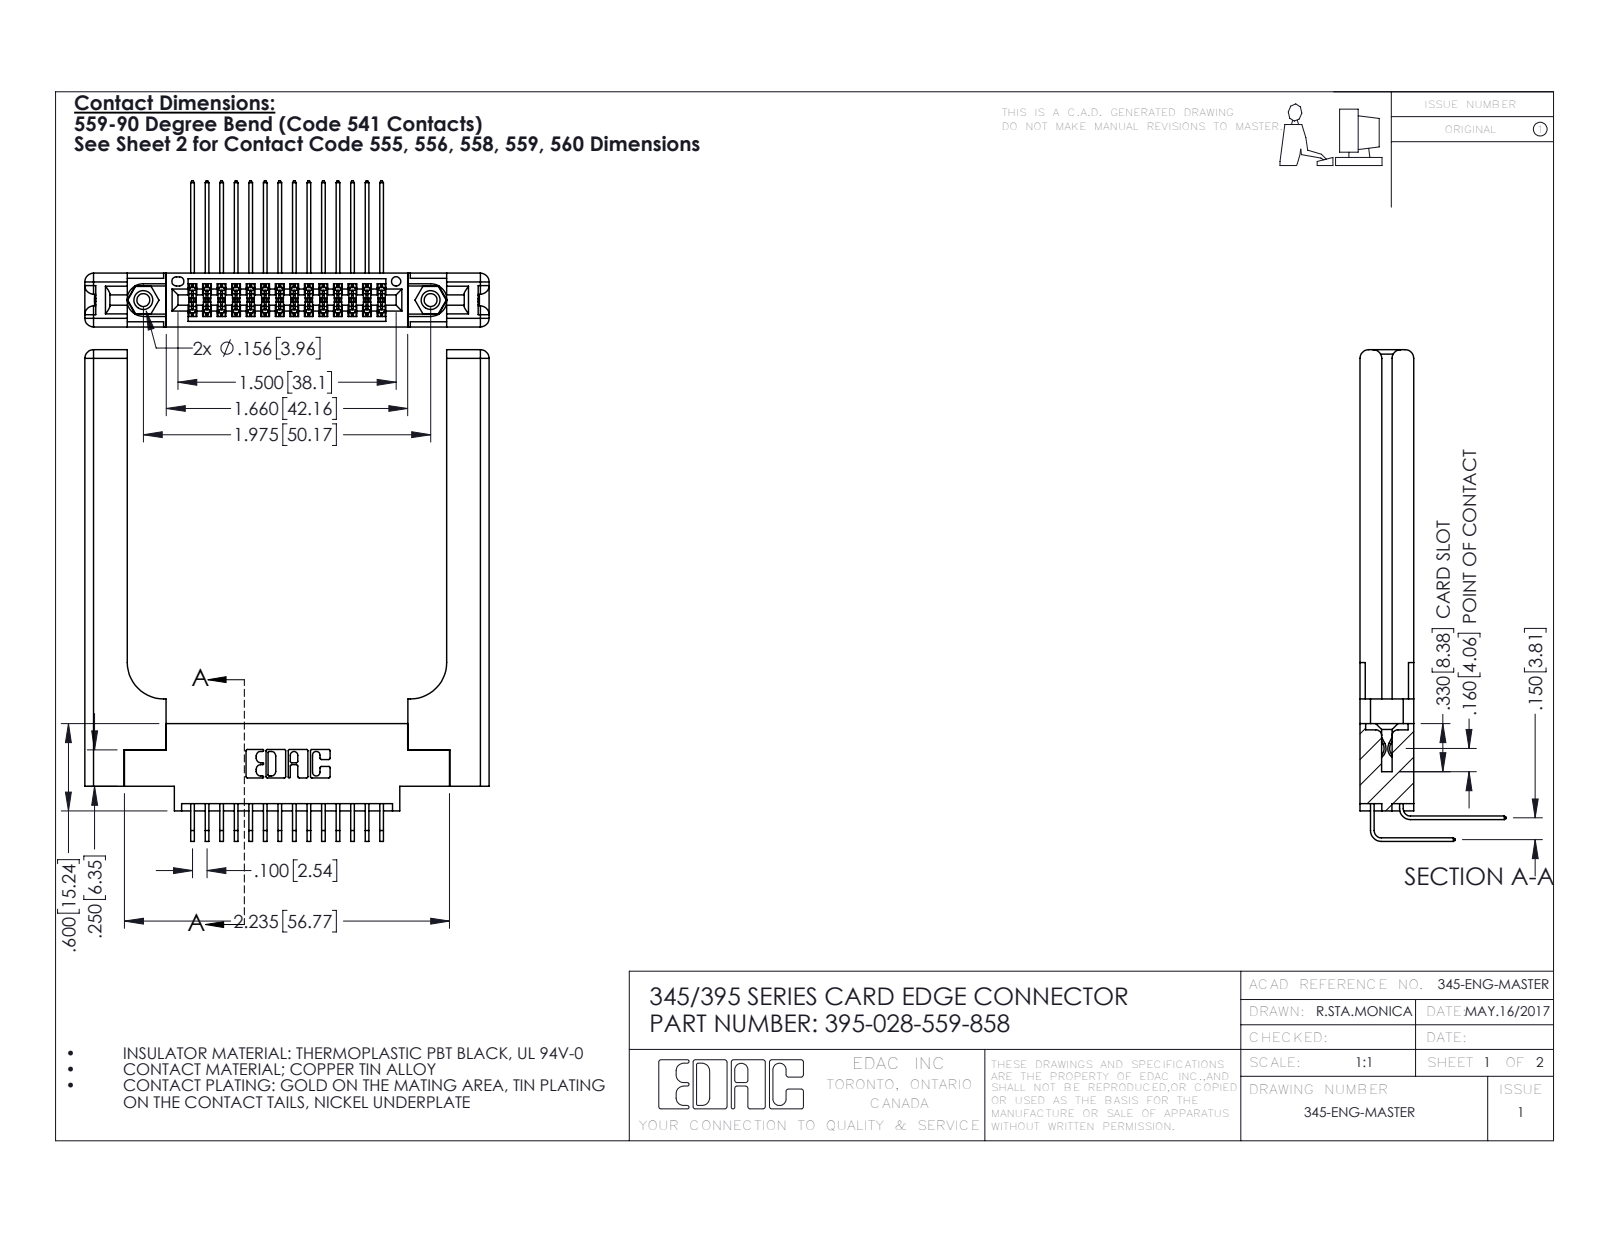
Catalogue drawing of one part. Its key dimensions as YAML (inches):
part_name: "345-220-058_345-220-058; 345-292-001_559 Tail - 2; 395-028-559-858; 345-292-001_558 559 Tail - 1 (+2 more)"
step_written_by: "SolidWorks 2016 (CONFIG_CONTROL_DESIGN)"
units: inches
bodies: {solids: 33, faces: 1842, planar: 1212, cylindrical: 570, other: 60}
overall_size: [3.379, 2.779, 1.005]
volume: 0.923
surface_area: 23.63
round_holes:
  - {diameter: 0.089, count: 2}
  - {diameter: 0.125, count: 2}
  - {diameter: 0.156, count: 2}
  - {diameter: 0.064, count: 1}
round_bosses_or_shafts:
  - {diameter: 0.155, count: 2}
partial_cylinders:
  - {radius: 0.006, count: 42}
  - {radius: 0.01, count: 22}
  - {radius: 0.06, count: 16}
  - {radius: 0.007, count: 6}
  - {radius: 0.031, count: 6}
  - {radius: 0.026, count: 3}
  - {radius: 0.014, count: 2}
  - {radius: 0.019, count: 2}
face_to_face_distances: [0.37, 0.072, 0.298, 0.148, 0.15, 0.077, 0.22, 0.225, 0.098, 0.272]
hole_center_spacings: [0.27, 1.742, 1.975]
